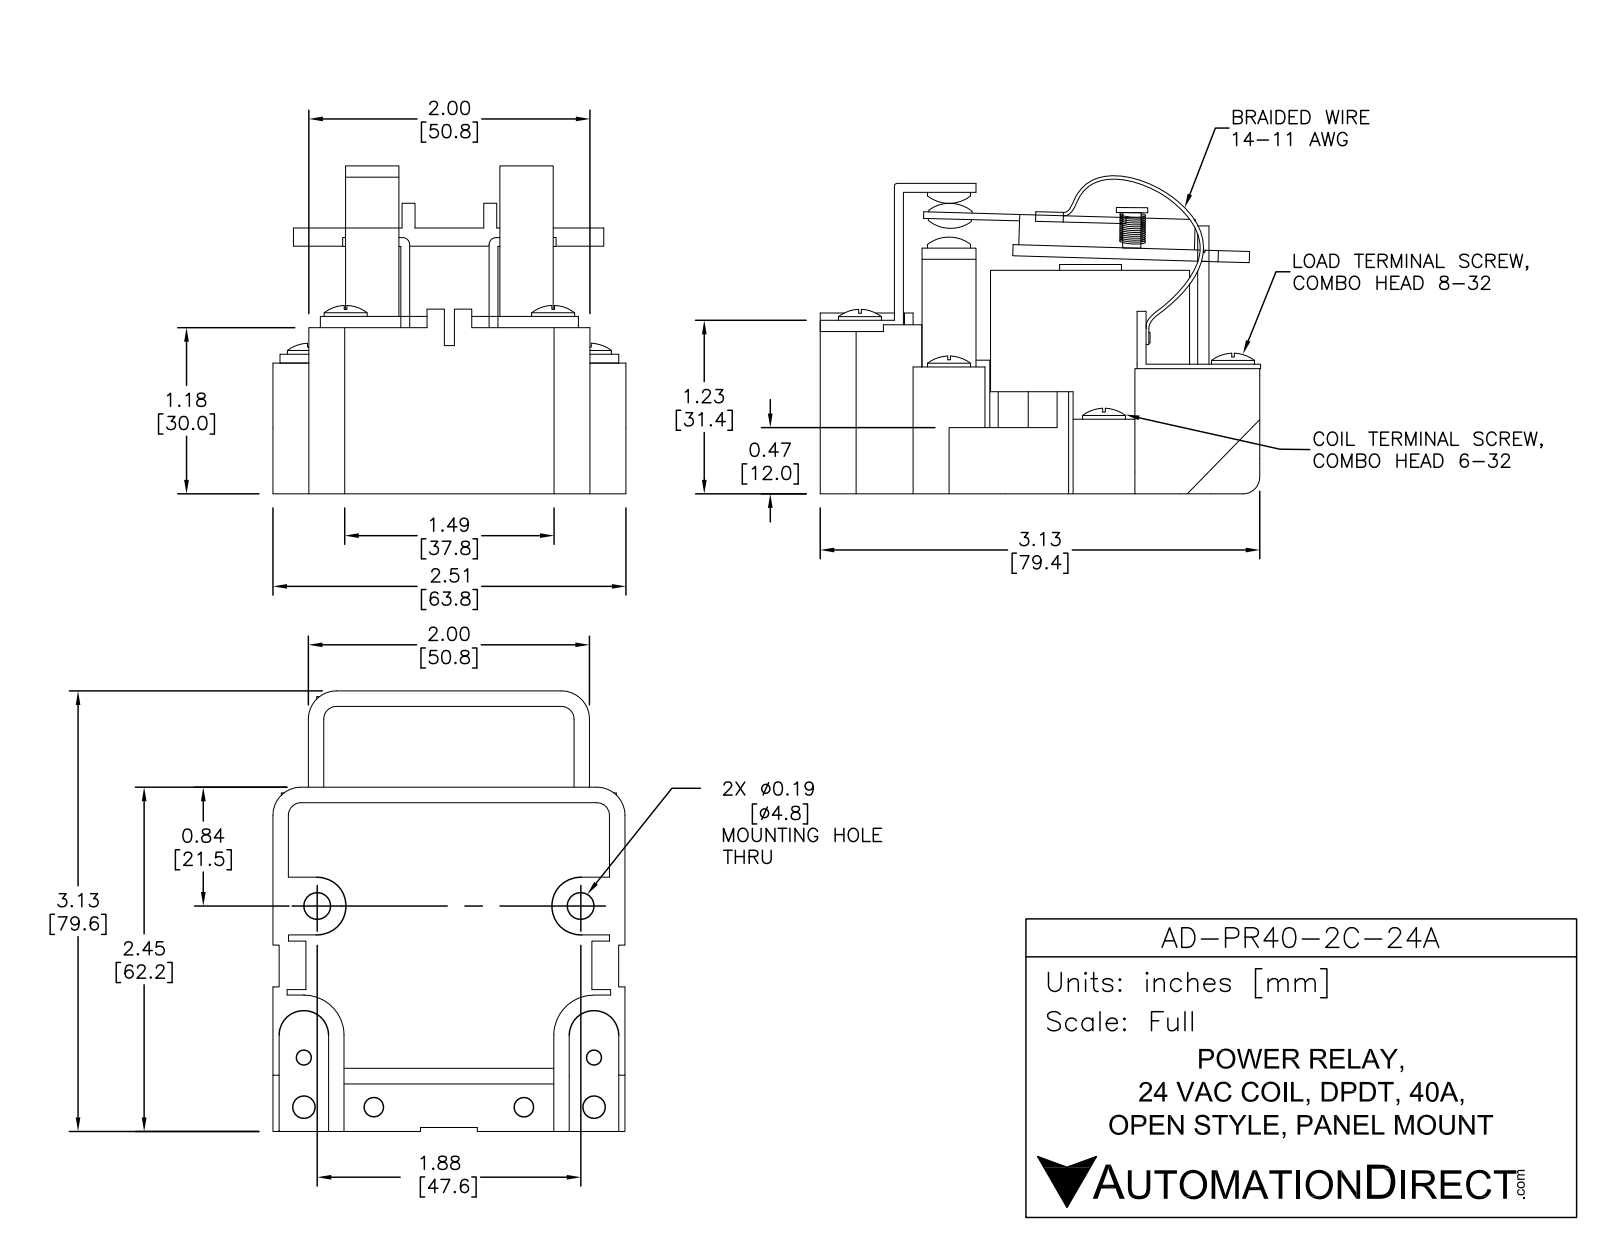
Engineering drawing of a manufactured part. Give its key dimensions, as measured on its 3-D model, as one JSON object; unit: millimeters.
{"part_name": "AD-PR40-2C-24A", "step_written_by": "SolidWorks 2013 (AUTOMOTIVE_DESIGN)", "units": "millimeters", "bodies": {"solids": 37, "faces": 861, "planar": 578, "cylindrical": 185, "other": 98}, "overall_size": [83.31, 64.94, 55.05], "volume_mm3": 127413, "surface_area_mm2": 42989, "round_holes": [[5, 4], [3.33, 2], [10, 2], [30, 1]], "round_bosses_or_shafts": [[7.75, 6], [6.5, 6], [5.28, 4], [6.85, 2], [5.5, 2], [3.5, 2], [35.5, 1], [18, 1]], "partial_cylinders_radius": [[1, 15], [0.75, 10], [3, 5], [5, 5], [0.38, 4], [1.48, 4], [1.5, 4], [7, 4]], "face_to_face_distances": [2, 1.5, 1, 10, 6.5, 4.5, 36.25, 12, 48.25, 3.5], "hole_center_spacings": [10, 26.2, 27.51, 29.92, 36.54, 37.51, 49.24, 50.25]}
